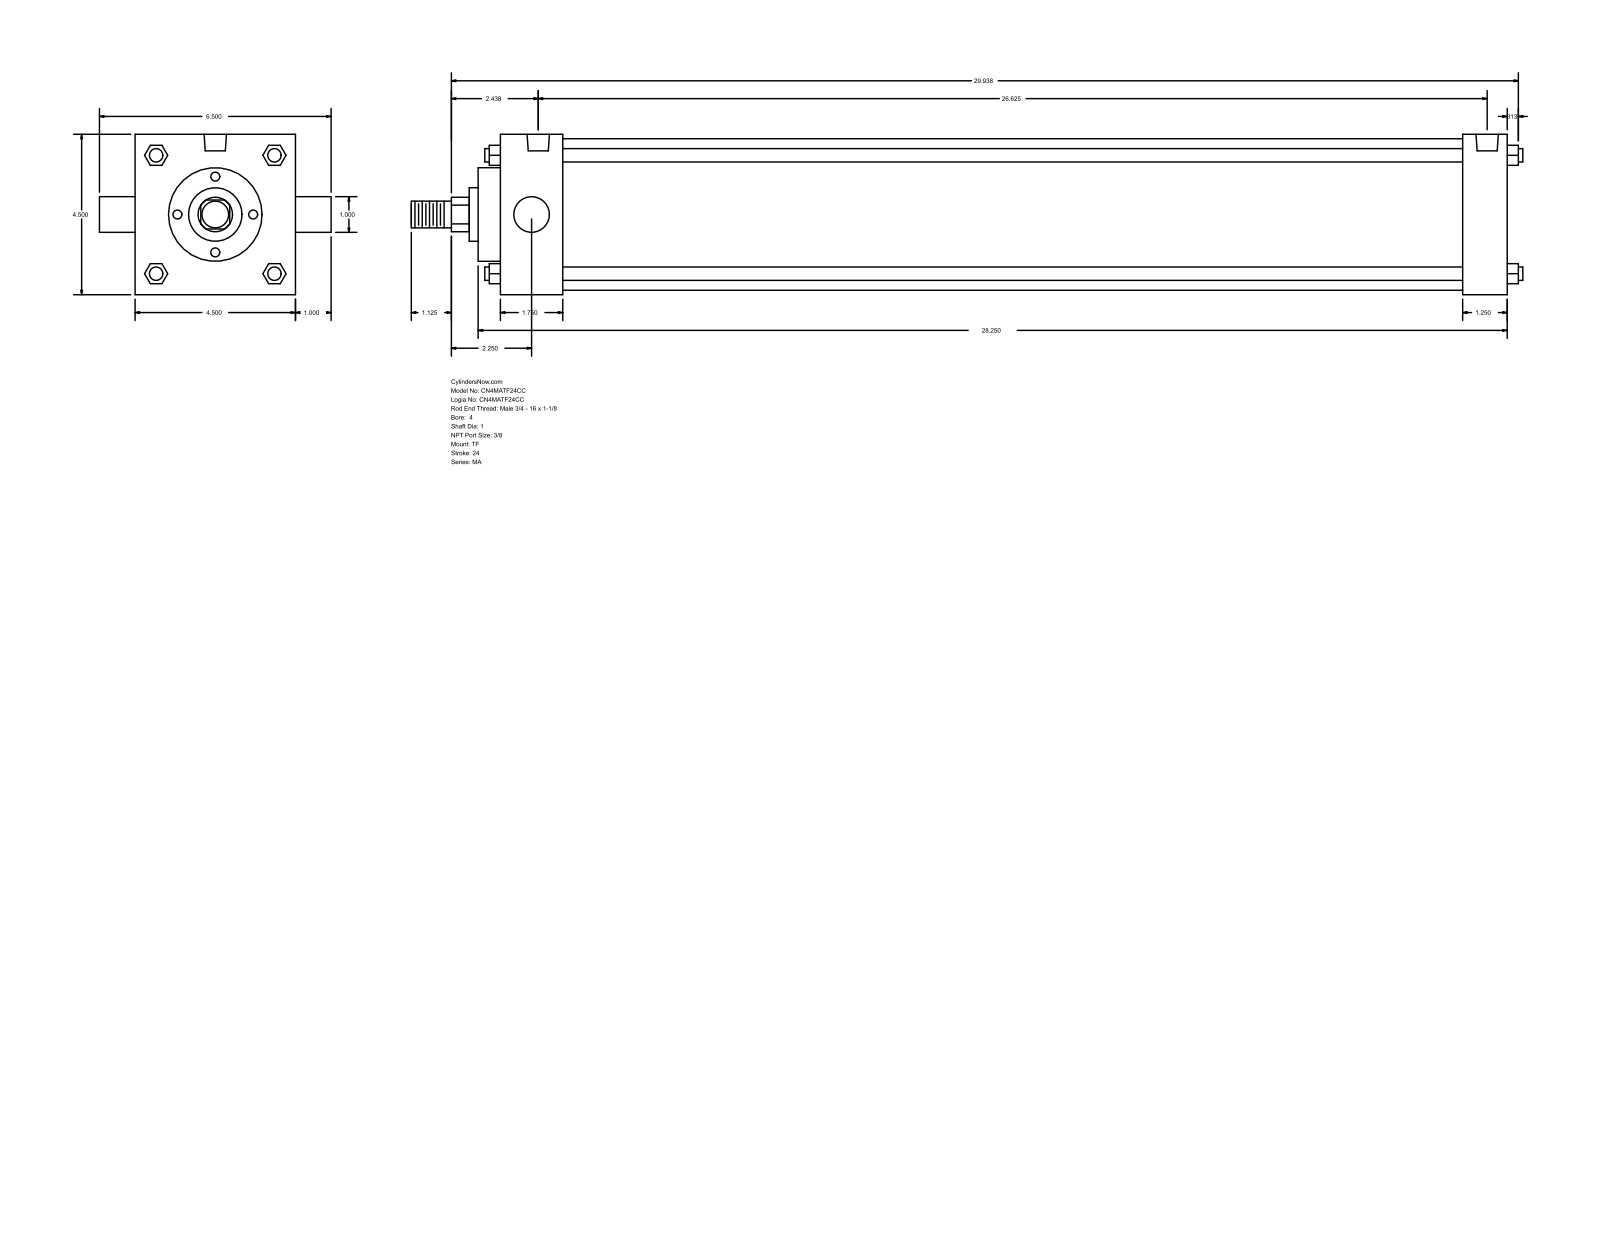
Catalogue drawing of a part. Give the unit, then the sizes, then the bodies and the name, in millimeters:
Units: millimetres
Overall size (bounding box): 792.16 × 165.1 × 114.3
Round holes (diameter × count): ⌀11.11 ×3, ⌀15.93 ×2
Round bosses / shafts (diameter × count): ⌀9.53 ×4, ⌀25.4 ×2, ⌀107.95 ×1, ⌀66.67 ×1, ⌀38.1 ×1, ⌀19.05 ×1
Partial cylindrical surfaces — rounded edges, fillets, slot ends (radius × count): R12.29 ×1
Main face-to-face distances: 114.3, 717.56, 685.81, 31.75, 44.46, 641.35, 673.1, 15.87, 60.33, 701.68
Hole centre spacings: 4.76, 4.77, 666.75, 671.51, 671.52, 676.28
Bodies: 0 solids, 122 faces (93 planar, 29 cylindrical, 0 other)
Part name (STEP PRODUCT): MA_TF__0400_1
STEP written by: GSSL Pune (CONFIG_CONTROL_DESIGN)
